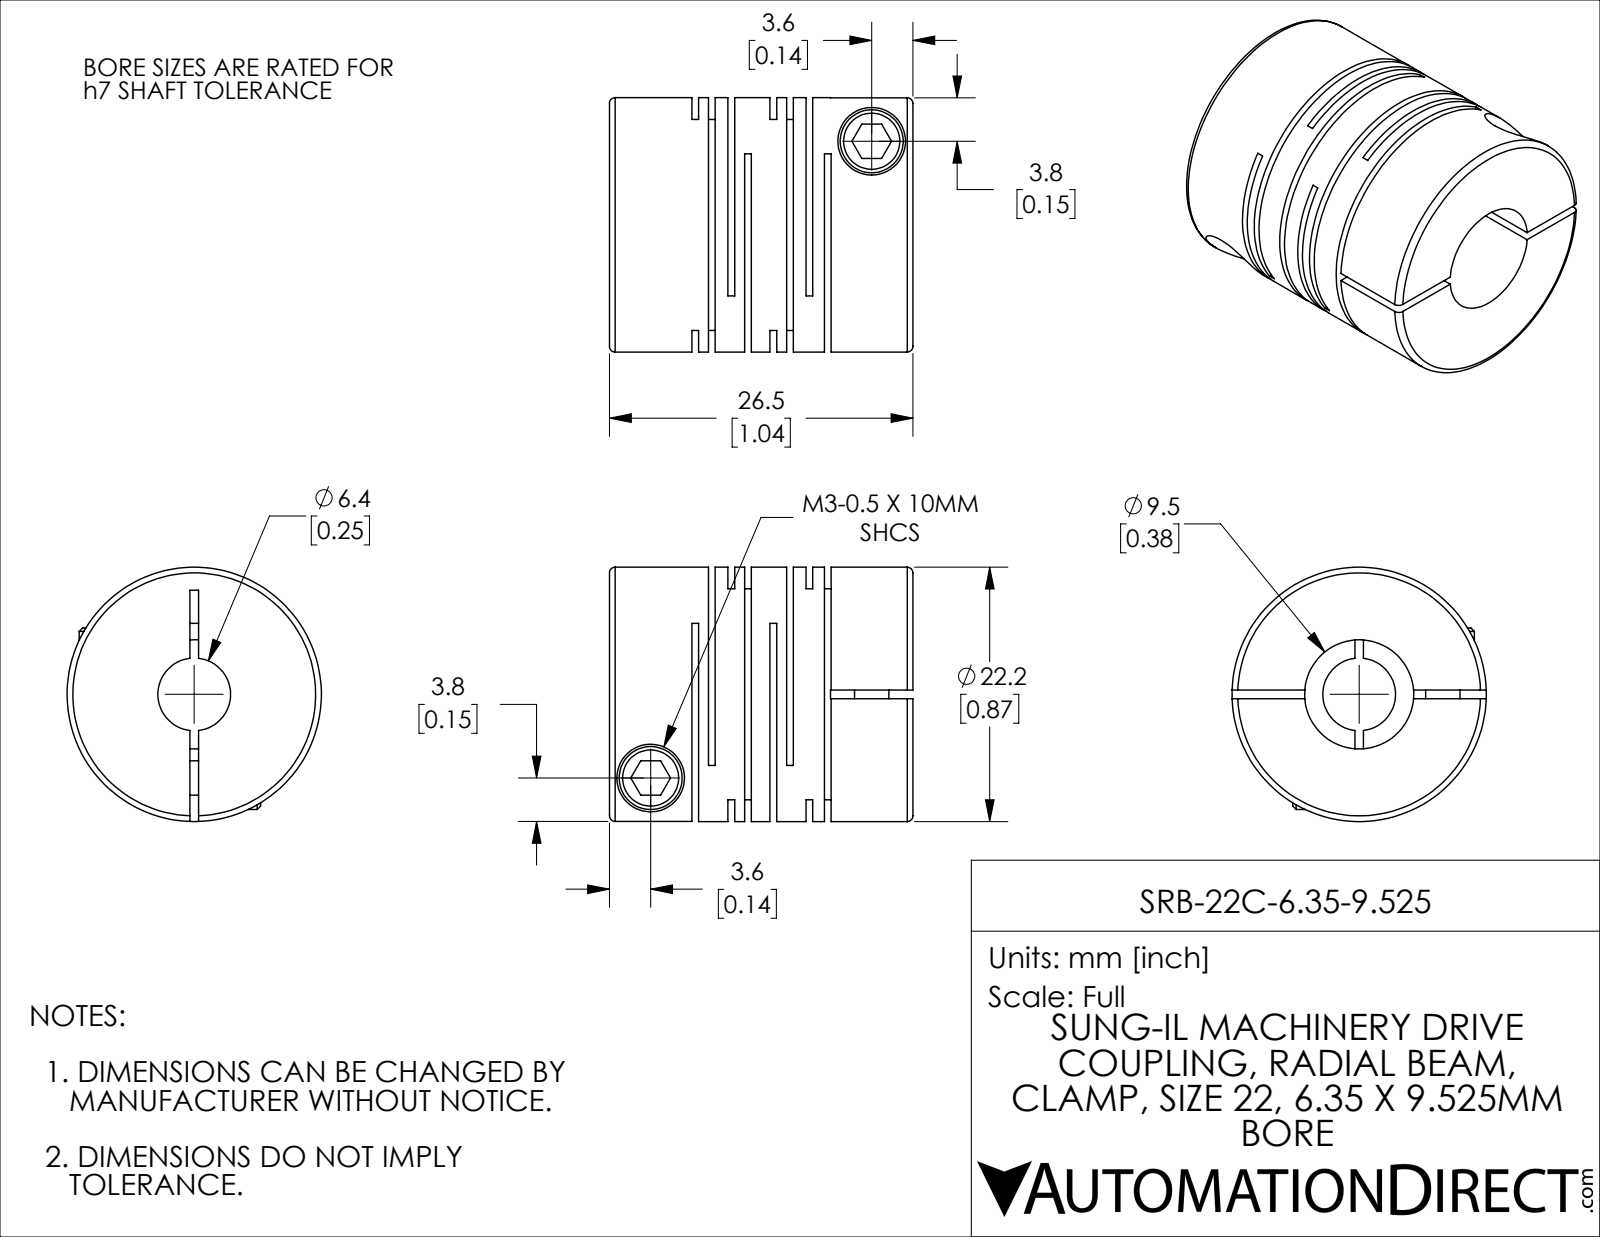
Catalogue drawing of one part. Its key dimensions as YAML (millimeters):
part_name: "SRB-22C-6.35-9.525"
step_written_by: "SolidWorks 2021 (CONFIG_CONTROL_DESIGN)"
units: millimeters
bodies: {solids: 1, faces: 115, planar: 60, cylindrical: 42, other: 13}
overall_size: [26.5, 22.2, 22.2]
volume: 7138
surface_area: 7595
round_holes:
  - {diameter: 3, count: 2}
  - {diameter: 5.9, count: 2}
  - {diameter: 6.35, count: 1}
  - {diameter: 9.53, count: 1}
round_bosses_or_shafts:
  - {diameter: 5.5, count: 2}
  - {diameter: 22.2, count: 1}
face_to_face_distances: [0.59, 6.82, 1.45, 3.15, 5.37, 3.67, 1.7, 7.41, 6.23, 2.04]
